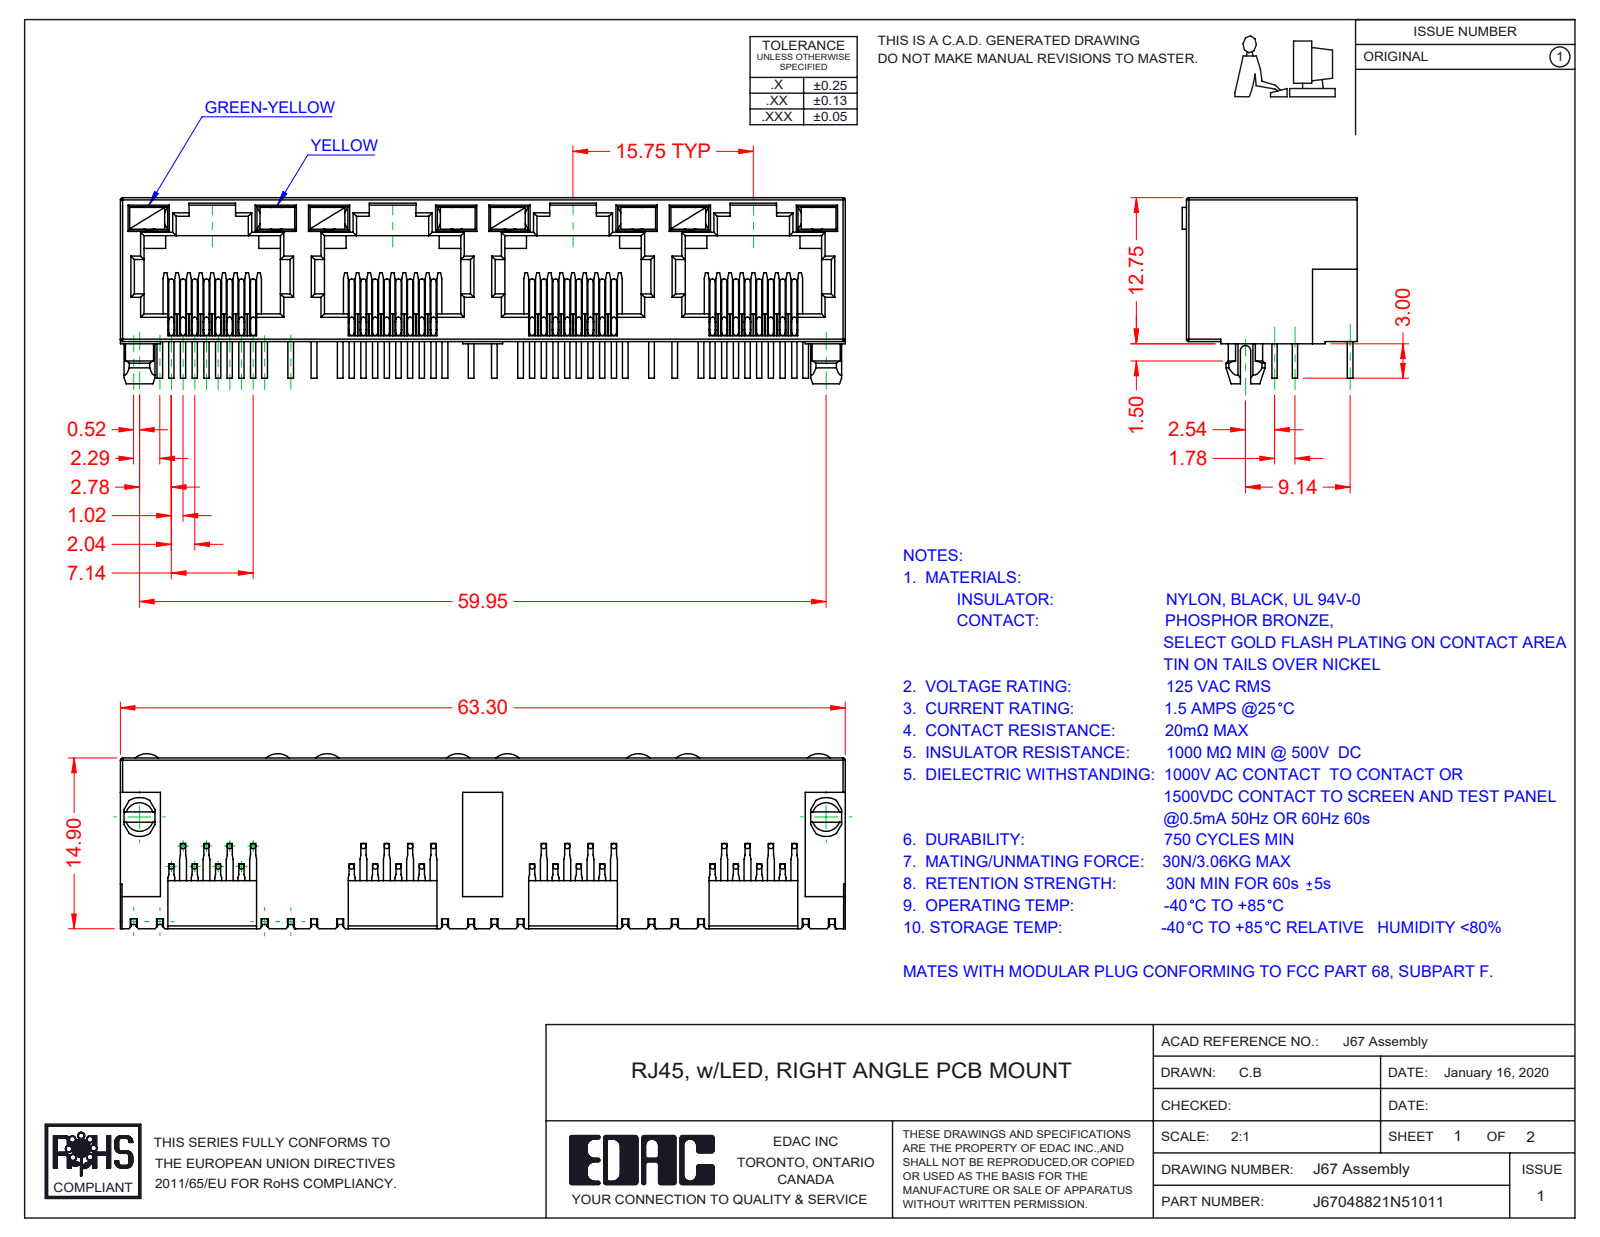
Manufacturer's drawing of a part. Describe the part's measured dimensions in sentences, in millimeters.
The part is named "67 Contacts; 67 LED LH_5-Green-Yellow; 67 LED RH_1-Yellow; J67048822N51011 (+1 more)". Its 3-D file was written by "SolidWorks 2016 (CONFIG_CONTROL_DESIGN)". It is 41 solids with 2473 faces: 1781 planar, 484 cylindrical and 208 other. Overall it measures 63.3 by 16.25 by 15.28 millimeters. Its volume is 5 159 cubic millimeters and its surface area 11 573 square millimeters. Round bosses or shafts: 96 of diameter 0.46. Partial cylindrical surfaces (rounded edges, fillets, slot ends): 66 of radius 0.2, 29 of radius 0.3, 9 of radius 0.45, 8 of radius 1.55, 2 of radius 1.5, 2 of radius 1.7, 1 of radius 0.35, 1 of radius 1. The main face-to-face distances are 0.5, 12.55, 1.89, 0.89, 10, 15.75, 1, 1.39, 11, 11.89.
